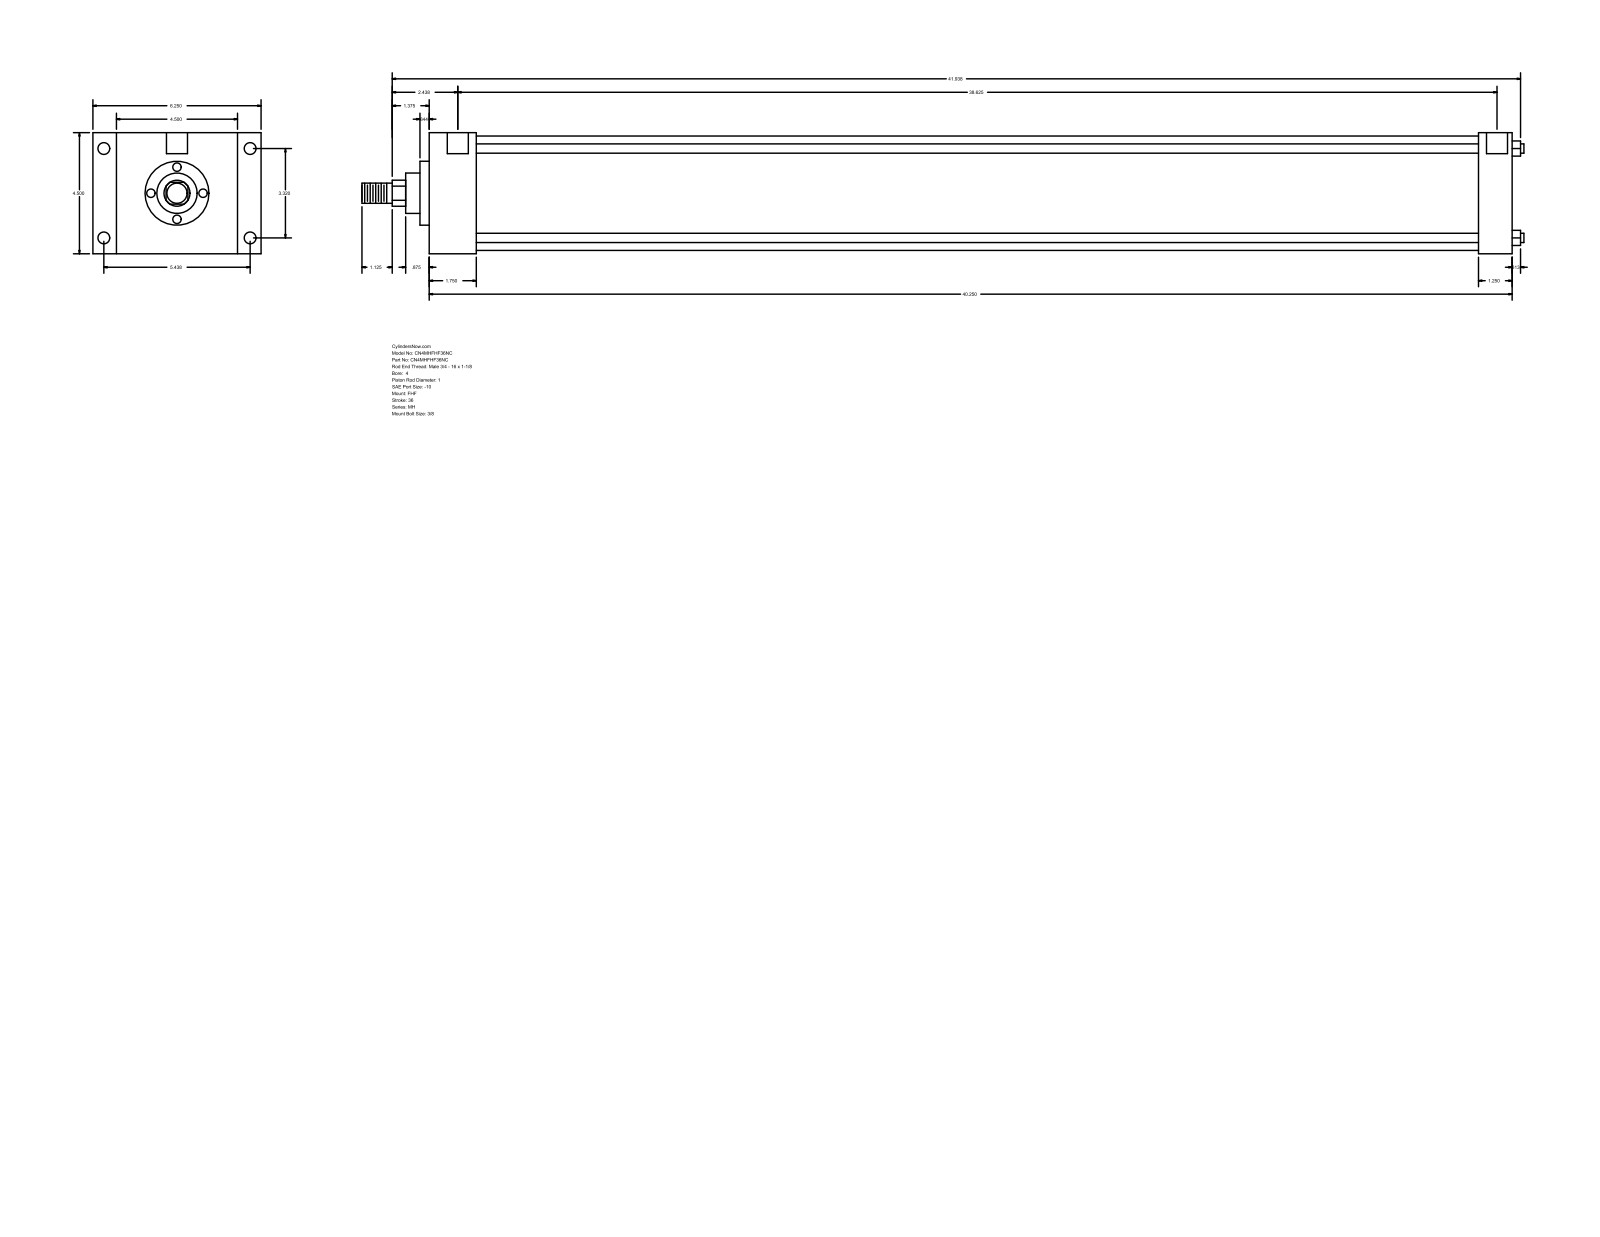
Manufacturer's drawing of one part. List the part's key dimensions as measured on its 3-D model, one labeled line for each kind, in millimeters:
Part name (STEP PRODUCT): MH_FHF__0400_1
STEP written by: GSSL Pune (CONFIG_CONTROL_DESIGN)
Units: millimetres
Bodies: 0 solids, 90 faces (61 planar, 29 cylindrical, 0 other)
Overall size (bounding box): 1096.96 × 158.75 × 114.3
Round holes (diameter × count): ⌀8.73 ×4, ⌀11.13 ×4, ⌀19.84 ×2
Round bosses / shafts (diameter × count): ⌀8.76 ×4, ⌀107.95 ×1, ⌀60.33 ×1, ⌀38.1 ×1, ⌀25.4 ×1, ⌀19.05 ×1
Partial cylindrical surfaces — rounded edges, fillets, slot ends (radius × count): R12.29 ×1
Main face-to-face distances: 114.3, 1022.36, 44.46, 977.9, 22.23, 136.53, 158.76, 990.61, 946.15, 31.75
Hole centre spacings: 84.32, 138.12, 161.82, 984.25, 1.58, 1.59, 981.08, 982.66
